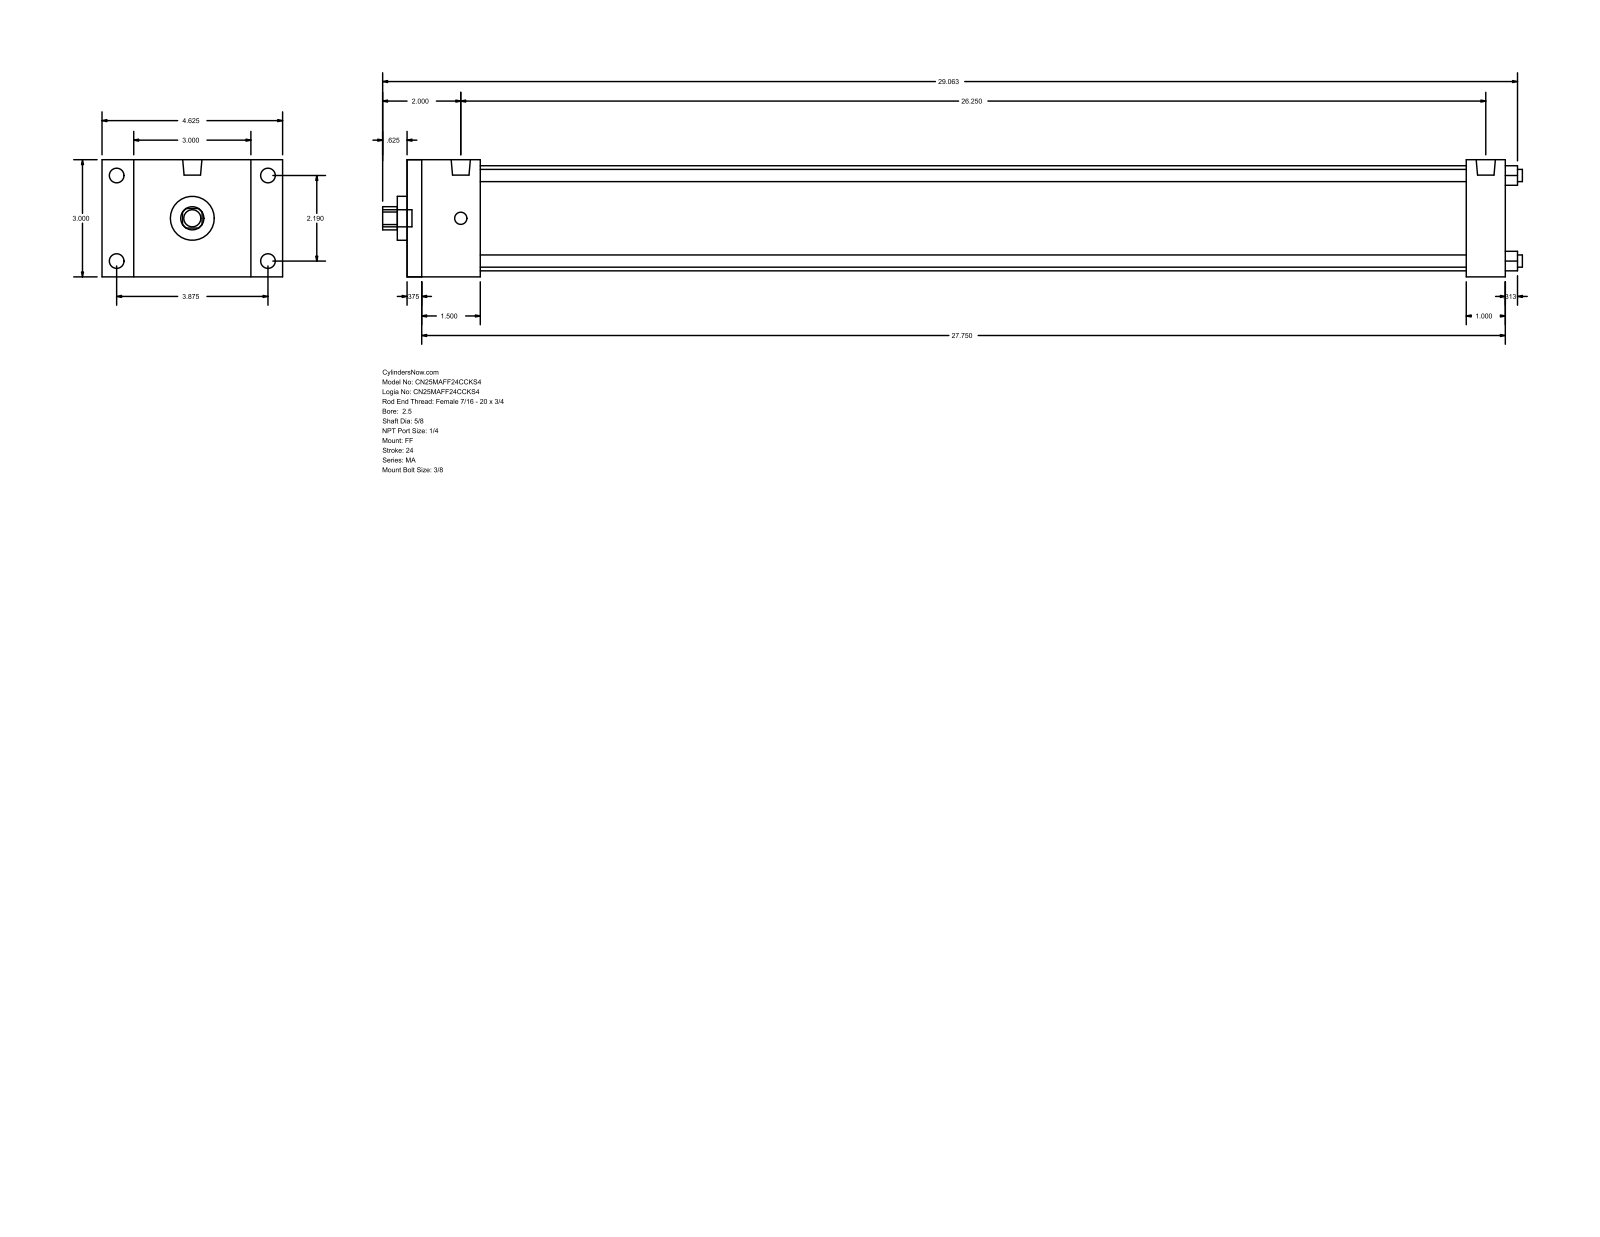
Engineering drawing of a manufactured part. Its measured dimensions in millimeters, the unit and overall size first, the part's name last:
Units: millimetres
Overall size (bounding box): 741.36 × 117.47 × 76.2
Round holes (diameter × count): ⌀7.94 ×4, ⌀15.88 ×1, ⌀28.57 ×1, ⌀68.33 ×1
Round bosses / shafts (diameter × count): ⌀9.53 ×4, ⌀7.94 ×4, ⌀12.49 ×2, ⌀11.11 ×1
Partial cylindrical surfaces — rounded edges, fillets, slot ends (radius × count): R7.54 ×1
Main face-to-face distances: 76.2, 714.37, 9.52, 704.85, 25.4, 47.62, 688.97, 38.1, 679.45, 641.35
Hole centre spacings: 39.33, 55.62, 78.66
Bodies: 0 solids, 92 faces (64 planar, 28 cylindrical, 0 other)
Part name (STEP PRODUCT): MA_FF__0250_0.625
STEP written by: GSSL Pune (CONFIG_CONTROL_DESIGN)
